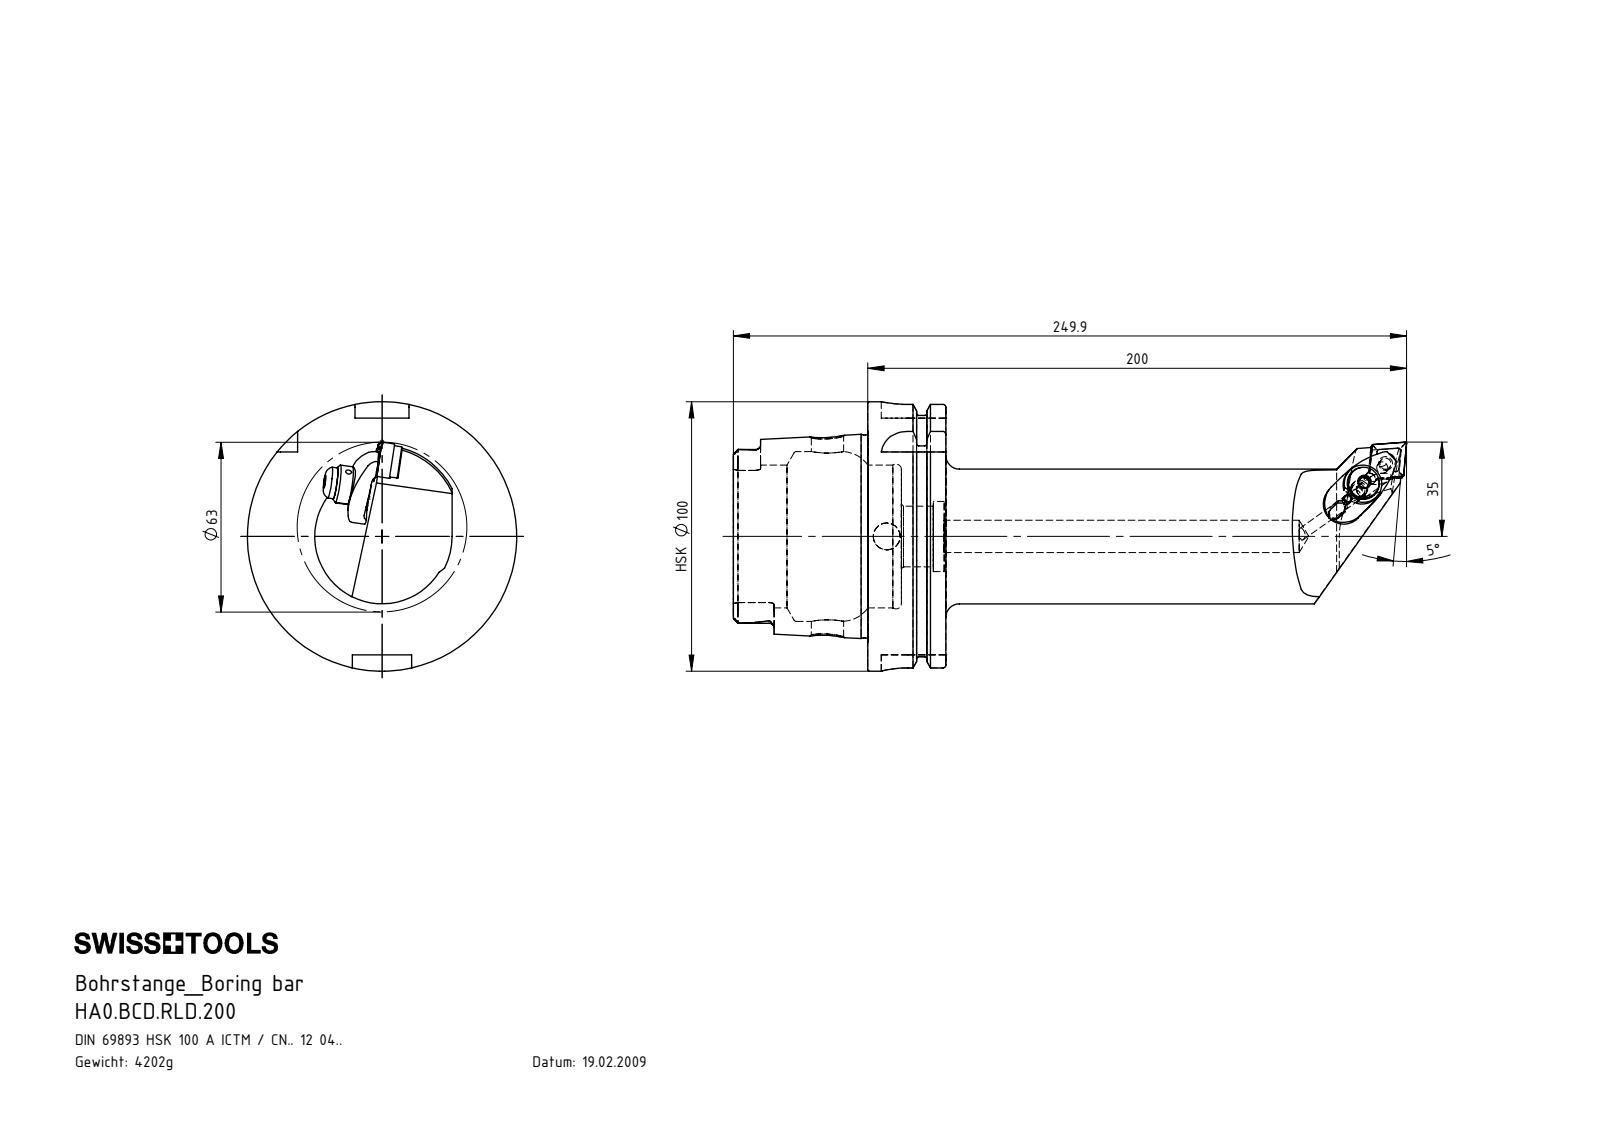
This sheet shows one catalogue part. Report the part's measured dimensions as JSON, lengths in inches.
{"part_name": "HA0-BCD.RLD.200; ISO 13337 - 3 x 12_PreviewCfg; WCC-ER5.102.012_B; KVT_MB_600_050 (+7 more)", "step_written_by": "SolidWorks 2012 (AUTOMOTIVE_DESIGN)", "units": "inches", "bodies": {"solids": 11, "faces": 461, "planar": 118, "cylindrical": 152, "other": 191}, "overall_size": [9.839, 3.937, 3.937], "volume_in3": 32.64, "surface_area_in2": 131.6, "round_holes": [[0.079, 3], [0.165, 3], [0.197, 2], [0.276, 2], [0.472, 2], [0.094, 1], [0.118, 1], [0.157, 1], [0.203, 1], [0.244, 1], [0.252, 1], [0.335, 1]], "round_bosses_or_shafts": [[0.197, 2], [0.118, 2], [3.937, 1], [3.62, 1], [2.963, 1], [1.969, 1], [0.551, 1], [0.453, 1]], "partial_cylinders_radius": [[0.015, 6], [0.027, 6], [0.075, 6], [0.016, 4], [0.039, 4], [0.394, 4], [0.059, 3], [0.079, 2]], "face_to_face_distances": [1.14, 0.49, 0.65, 1.965, 2.455, 3.104, 3.457, 3.079, 1.114, 0.624], "hole_center_spacings": [0.263, 0.315, 0.315, 0.323, 0.578, 0.591, 0.903, 0.906]}
